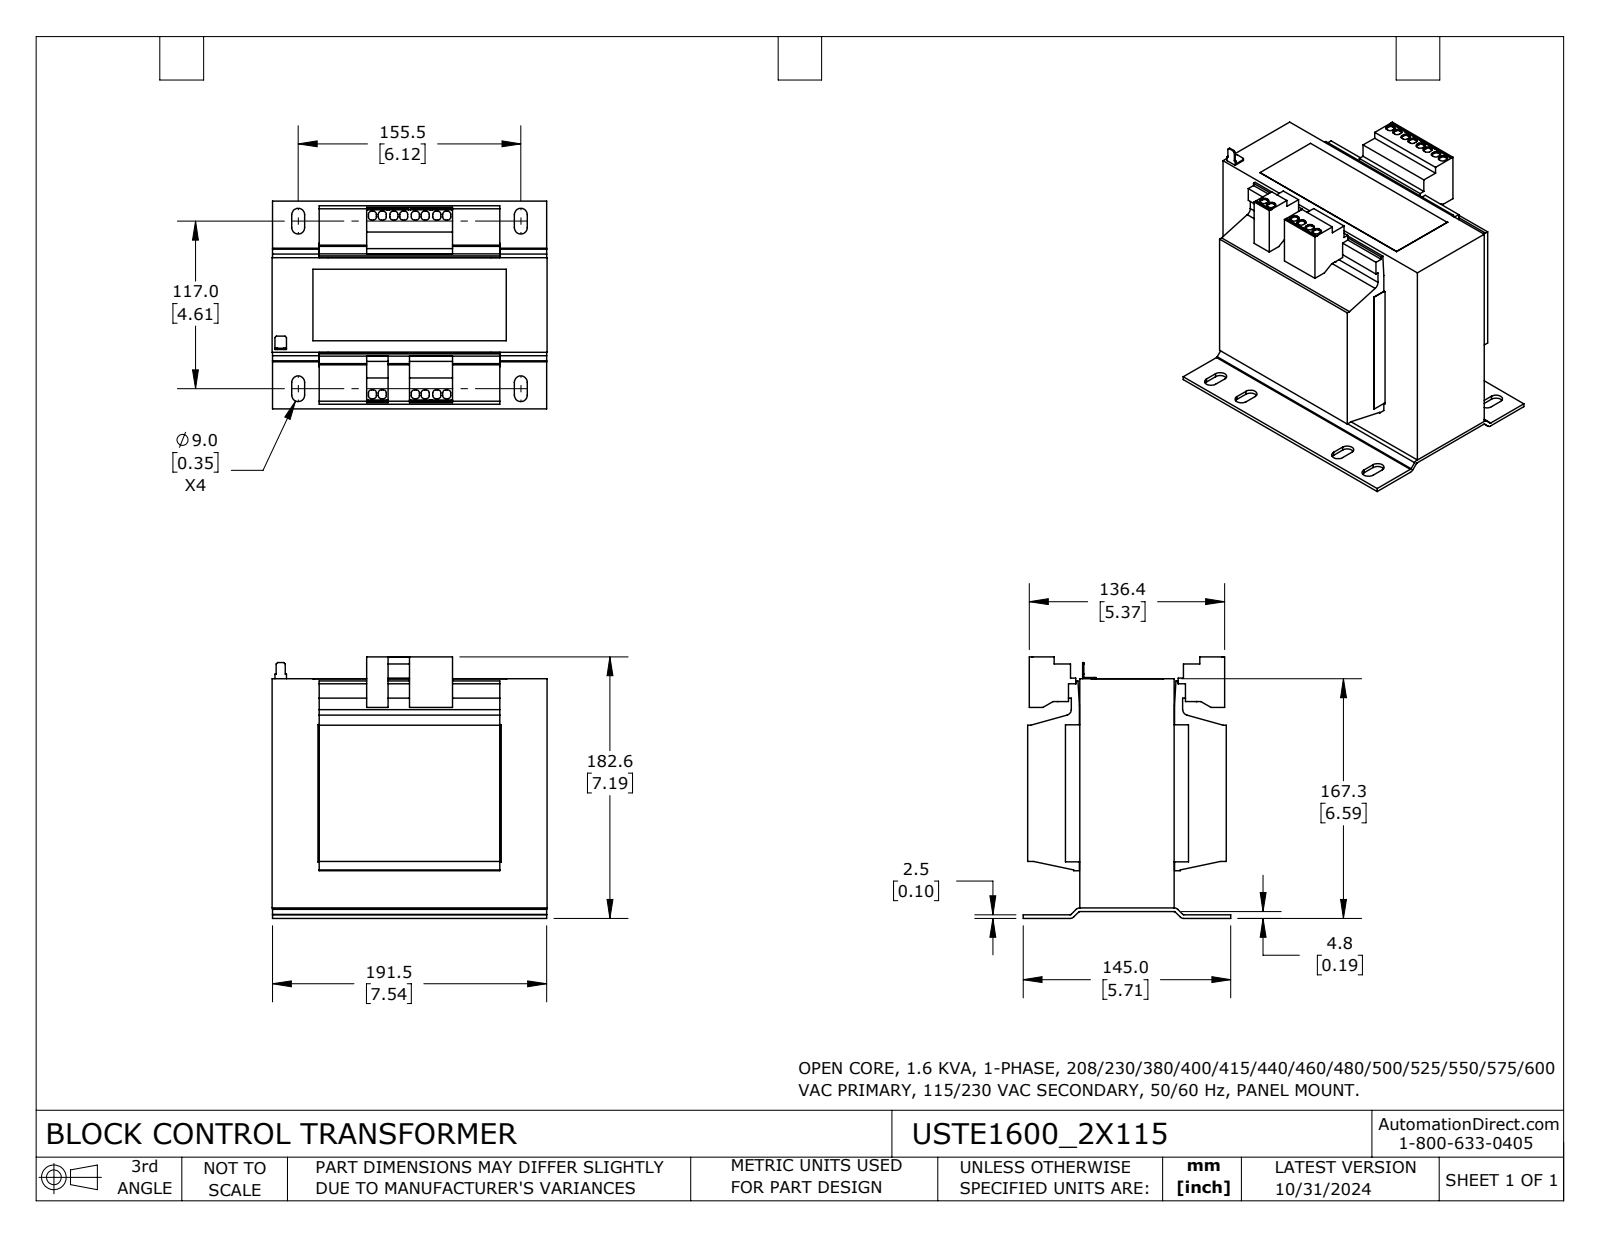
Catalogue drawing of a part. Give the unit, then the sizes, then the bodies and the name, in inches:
Units: inches
Overall size (bounding box): 7.559 × 7.19 × 5.709
Partial cylindrical surfaces — rounded edges, fillets, slot ends (radius × count): R0.087 ×56, R0.177 ×16, R0.039 ×4, R0.138 ×4, R0.157 ×2
Main face-to-face distances: 1.429, 4.028, 2.598, 1.26, 1.29, 6.269, 0.098, 6.299, 0.03, 5.009
Volume: 191.1 in³ · Surface area: 406.4 in²
Bodies: 1 solid, 469 faces (383 planar, 86 cylindrical, 0 other)
Part name (STEP PRODUCT): USTE1600_2X115
STEP written by: SolidWorks 2023 (CONFIG_CONTROL_DESIGN)
